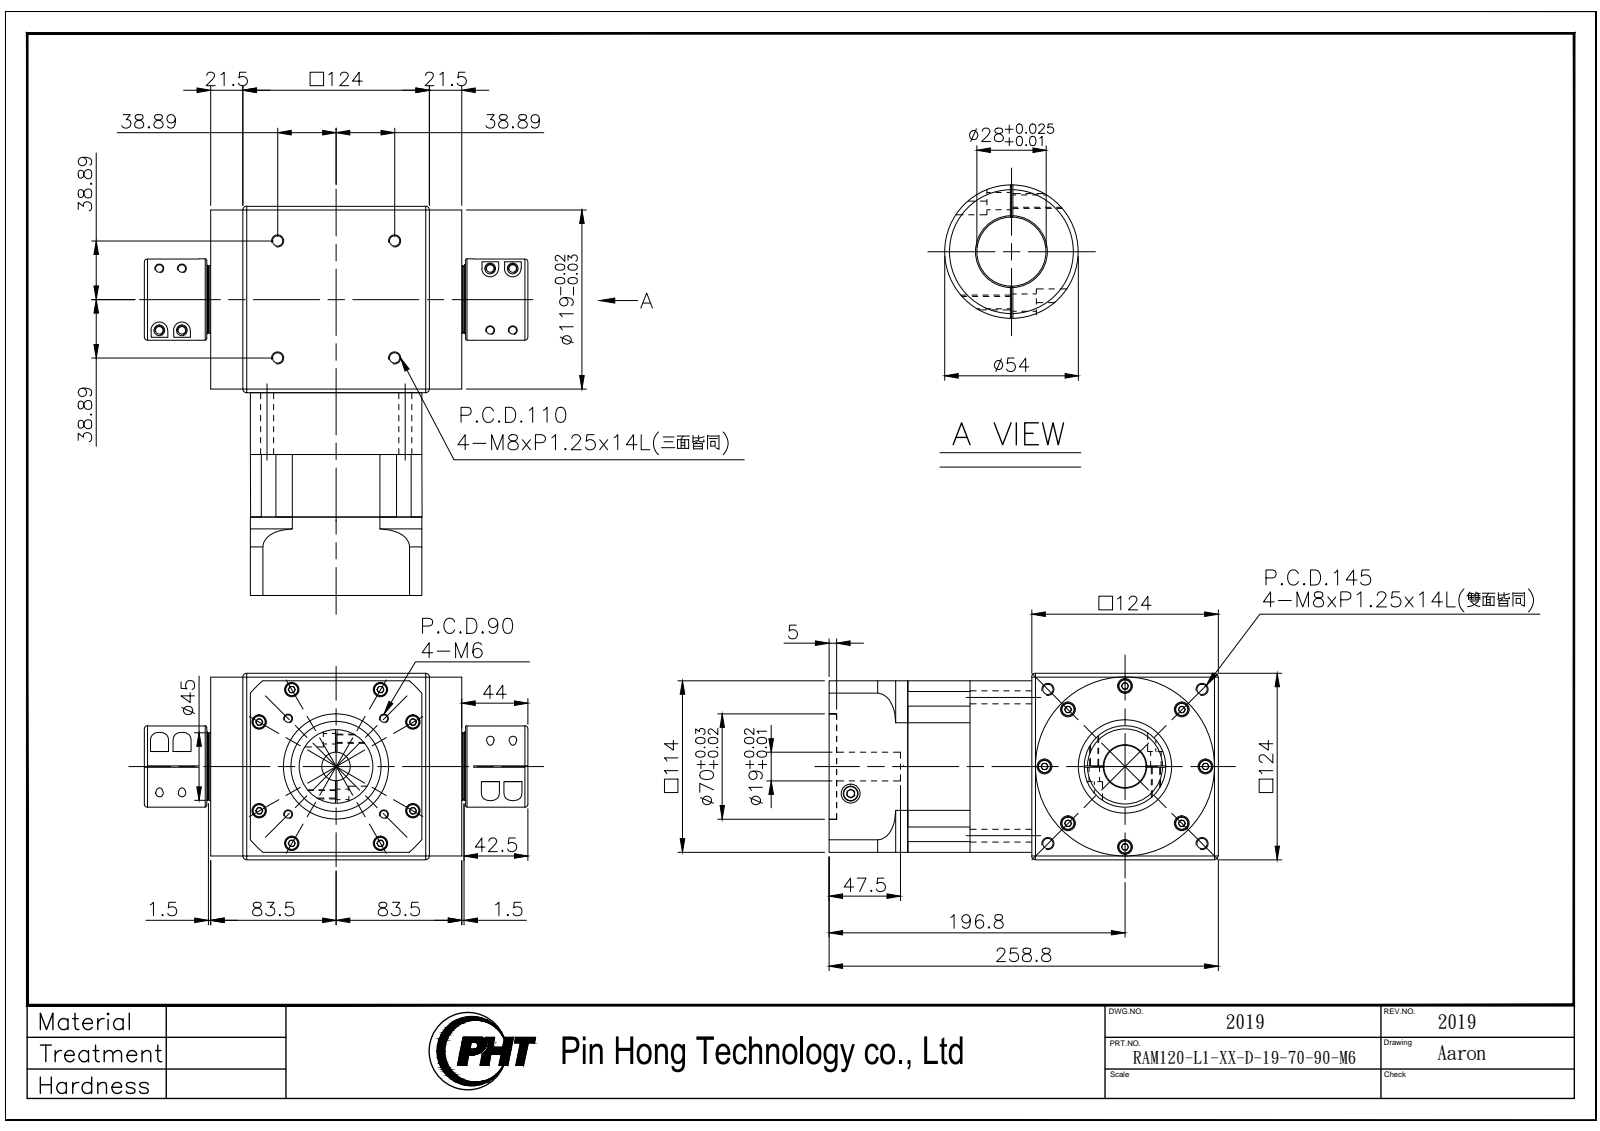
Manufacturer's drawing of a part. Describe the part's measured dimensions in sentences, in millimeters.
The part is named "RAM120-L1-XX-D-19-70-90-M6_2019". Its 3-D file was written by "SolidWorks 2016 (AUTOMOTIVE_DESIGN)". It is 4 solids with 1269 faces: 647 planar, 398 cylindrical and 224 other. Overall it measures 258.8 by 255 by 124 millimeters. Its volume is 3 916 000 cubic millimeters and its surface area 364 006 square millimeters. Round holes: 12 of diameter 6.8, 8 of diameter 5.3, 8 of diameter 7, 8 of diameter 9, 8 of diameter 9.5, 8 of diameter 14, 4 of diameter 5, 4 of diameter 8.6, 2 of diameter 12.7, 1 of diameter 19, 1 of diameter 28, 1 of diameter 32. Round bosses or shafts: 12 of diameter 13, 8 of diameter 10.5, 8 of diameter 10, 8 of diameter 8.5, 8 of diameter 6, 1 of diameter 119, 1 of diameter 110, 1 of diameter 62. Partial cylindrical surfaces (rounded edges, fillets, slot ends): 8 of radius 3.52, 8 of radius 5.5, 4 of radius 7, 1 of radius 64, 1 of radius 75, 1 of radius 86.2. The main face-to-face distances are 124, 5, 119, 41.5, 114, 82.5, 41, 206.5, 165, 26.5. The hole center spacings are 59, 10, 15.4, 17.24, 19.42, 39.8, 51.28, 52.
